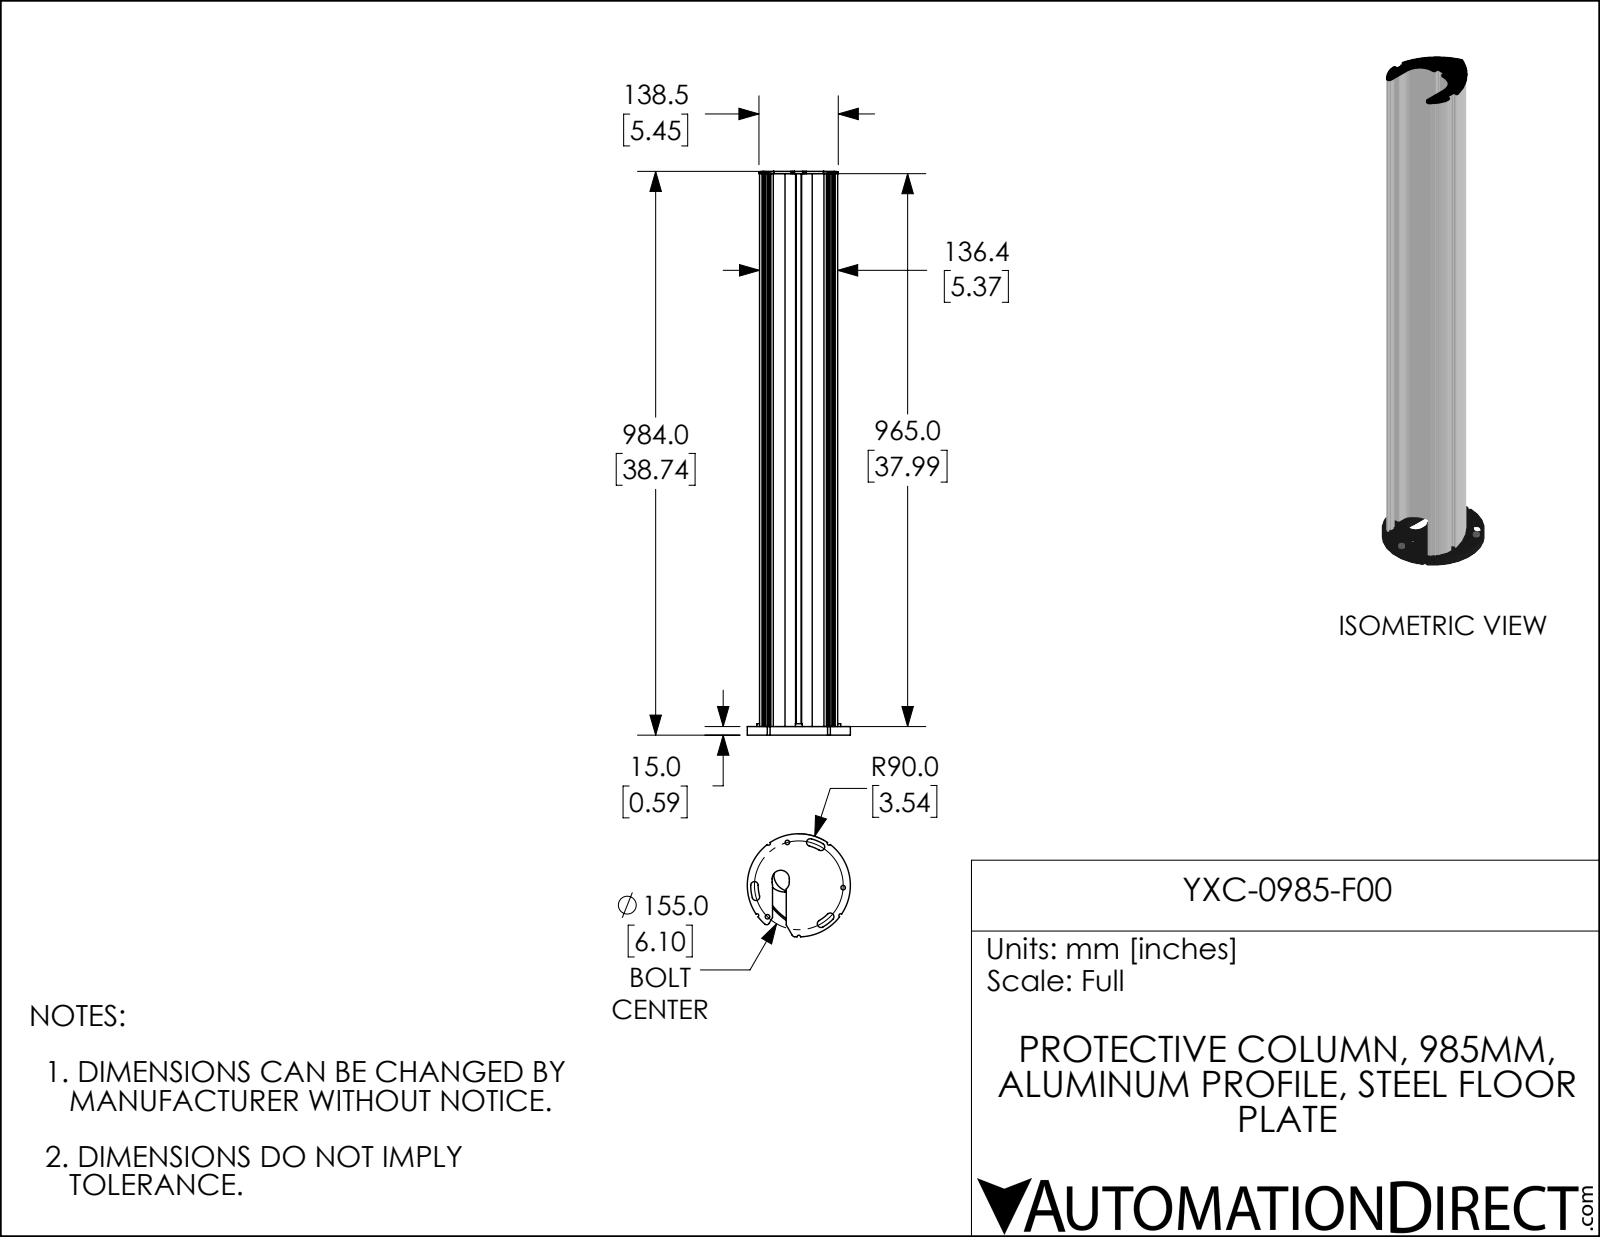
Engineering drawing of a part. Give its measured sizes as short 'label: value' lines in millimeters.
name: YXC-0985-F00
written by: SolidWorks 2019 (AUTOMOTIVE_DESIGN)
unit: mm
bodies: 1 solid, 326 faces (201 planar, 112 cylindrical, 13 other)
size: 984 × 180 × 180
volume: 5 791 000 mm³; area: 784 500 mm²
holes: 3× ⌀7.8, 1× ⌀4.4, 1× ⌀15
bosses: 3× ⌀12, 2× ⌀7.4, 1× ⌀180
rounds: 17× R3, 6× R1, 6× R1.3, 6× R6.5, 4× R15, 3× R5, 3× R6, 2× R1.5
face distances: 11.5, 3, 124.9, 19.7, 116.7, 8.2, 105.2, 8.5, 127.9, 11.2
hole spacings: 31.9, 31.9, 94.4, 94.5, 118.3, 118.3, 125.4, 134.2
